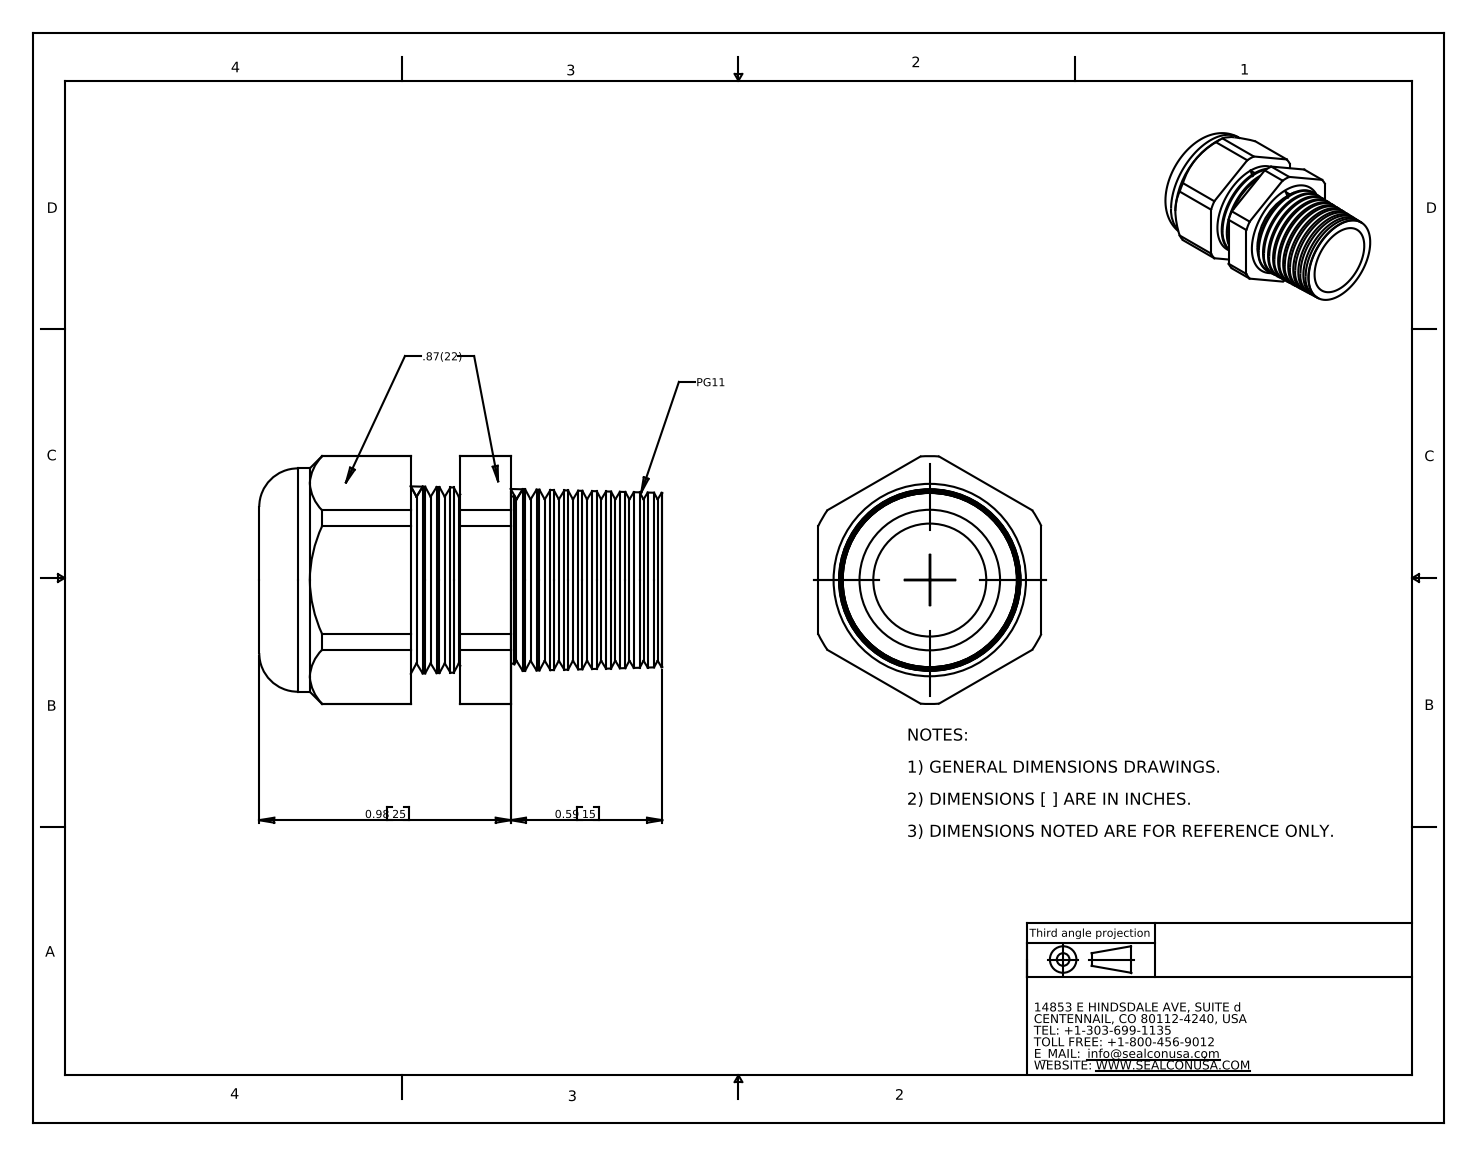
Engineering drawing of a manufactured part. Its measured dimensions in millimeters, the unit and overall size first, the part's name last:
Units: millimetres
Overall size (bounding box): 39.9 × 24.5 × 22.1
Round holes (diameter × count): ⌀11.2 ×1, ⌀13.9 ×1
Round bosses / shafts (diameter × count): ⌀22.1 ×1
Partial cylindrical surfaces — rounded edges, fillets, slot ends (radius × count): R12.3 ×1
Main face-to-face distances: 22.1, 4.9, 5, 9.9, 19.9, 10, 14.9, 34.9, 24.9, 20
Volume: 7 960 mm³ · Surface area: 6 174 mm²
Bodies: 2 solids, 148 faces (20 planar, 22 cylindrical, 106 other)
Part name (STEP PRODUCT): CD11CA-BK
STEP written by: SolidWorks 2007 (CONFIG_CONTROL_DESIGN)
